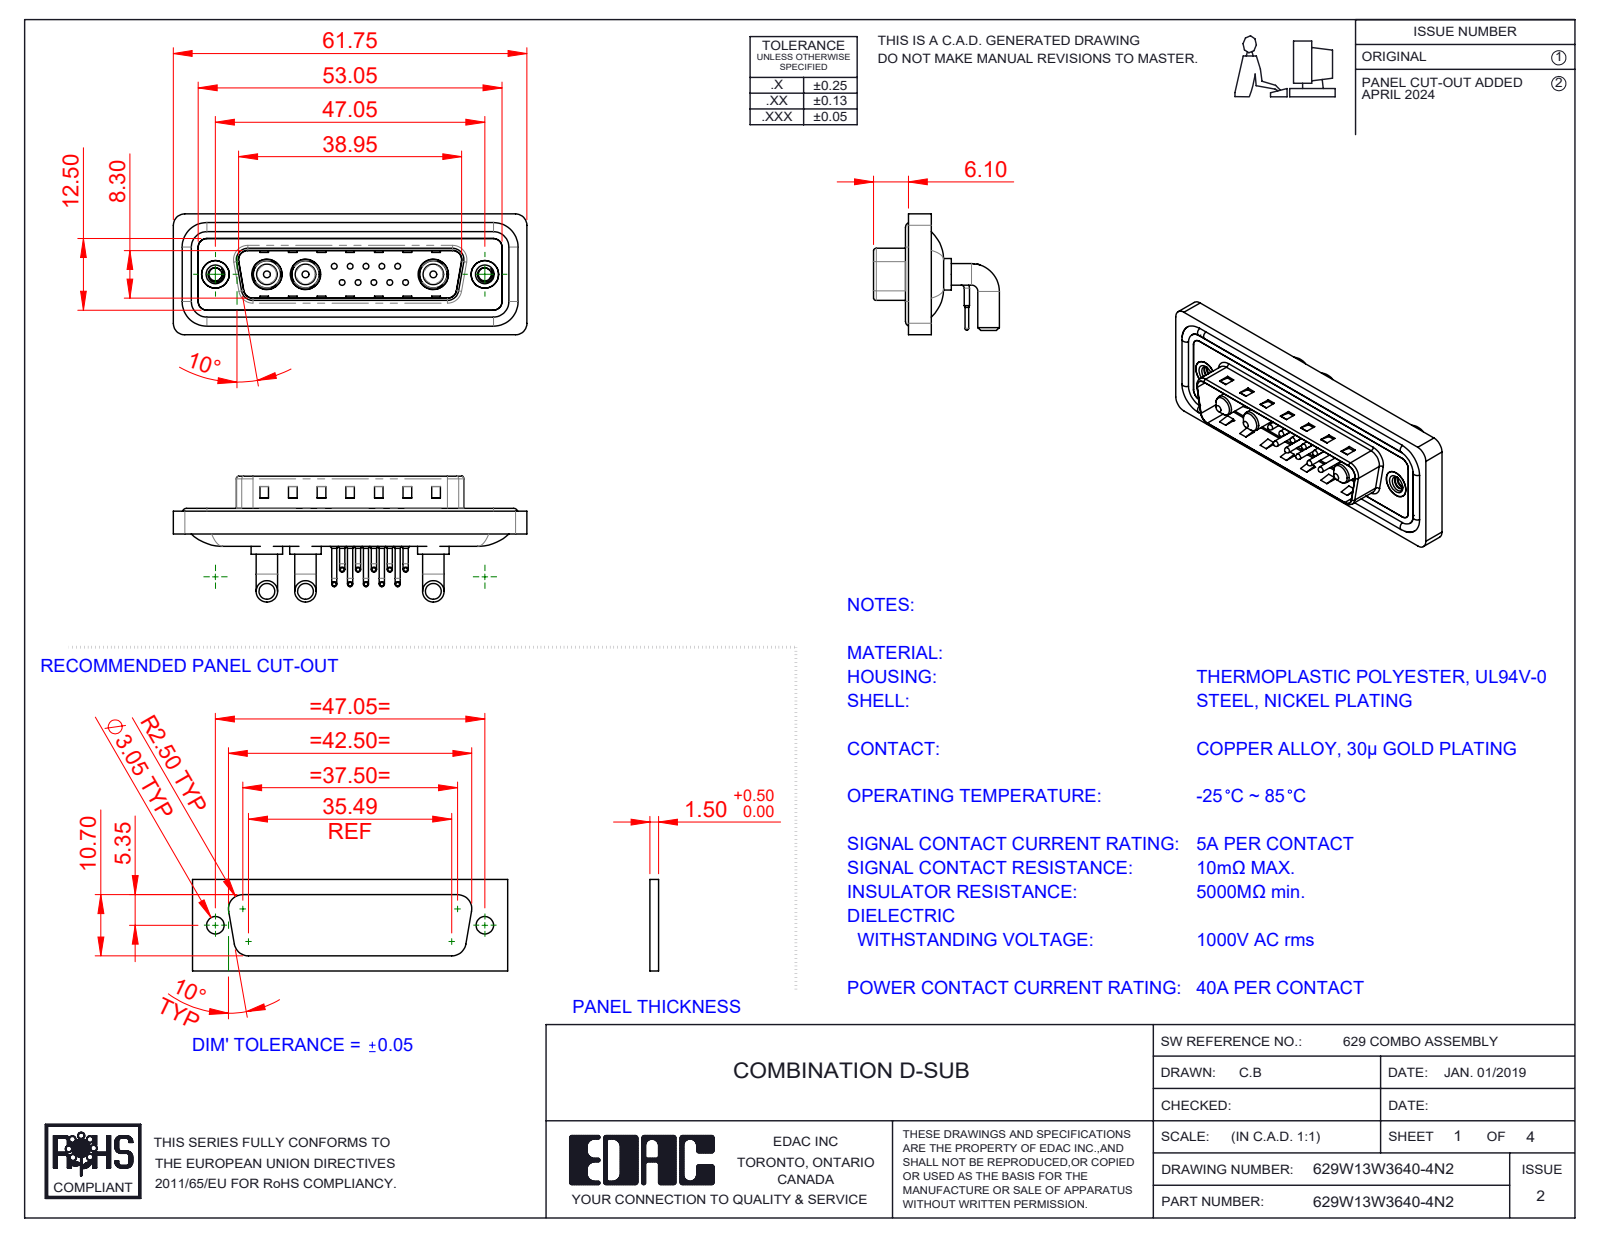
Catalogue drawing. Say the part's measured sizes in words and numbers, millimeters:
The part is named "629Combo Shell Front_25 Contacts; 629Combo Contact Row 2; 629Combo Shell Rear_25 Contacts; Power Pin_40A RA (+5 more)". Its 3-D file was written by "SolidWorks 2023 (CONFIG_CONTROL_DESIGN)". It is 23 solids with 1712 faces: 879 planar, 611 cylindrical and 222 other. Overall it measures 61.75 by 21.98 by 21.1 millimeters. Its volume is 7 840 cubic millimeters and its surface area 12 628 square millimeters. Round holes: 10 of diameter 0.75, 10 of diameter 1.6, 10 of diameter 2, 3 of diameter 4.85, 3 of diameter 5.3, 2 of diameter 2.26, 2 of diameter 4, 2 of diameter 4.8, 2 of diameter 5. Round bosses or shafts: 20 of diameter 0.9, 10 of diameter 1.5, 10 of diameter 1, 10 of diameter 0.65, 6 of diameter 3.75, 4 of diameter 1.6, 3 of diameter 5.5, 3 of diameter 5.2. Partial cylindrical surfaces (rounded edges, fillets, slot ends): 18 of radius 1.5, 18 of radius 2, 10 of radius 1.01, 8 of radius 0.5, 8 of radius 1.6, 4 of radius 0.25, 4 of radius 0.6, 4 of radius 0.65. The main face-to-face distances are 0.4, 2.9, 0.8, 4.1, 1.1, 2.1, 1.6, 4.5, 2.5, 1.5. The hole center spacings are 3.16, 2.77, 5.04, 5.54, 7.49, 5.03, 8.31, 10.11.
